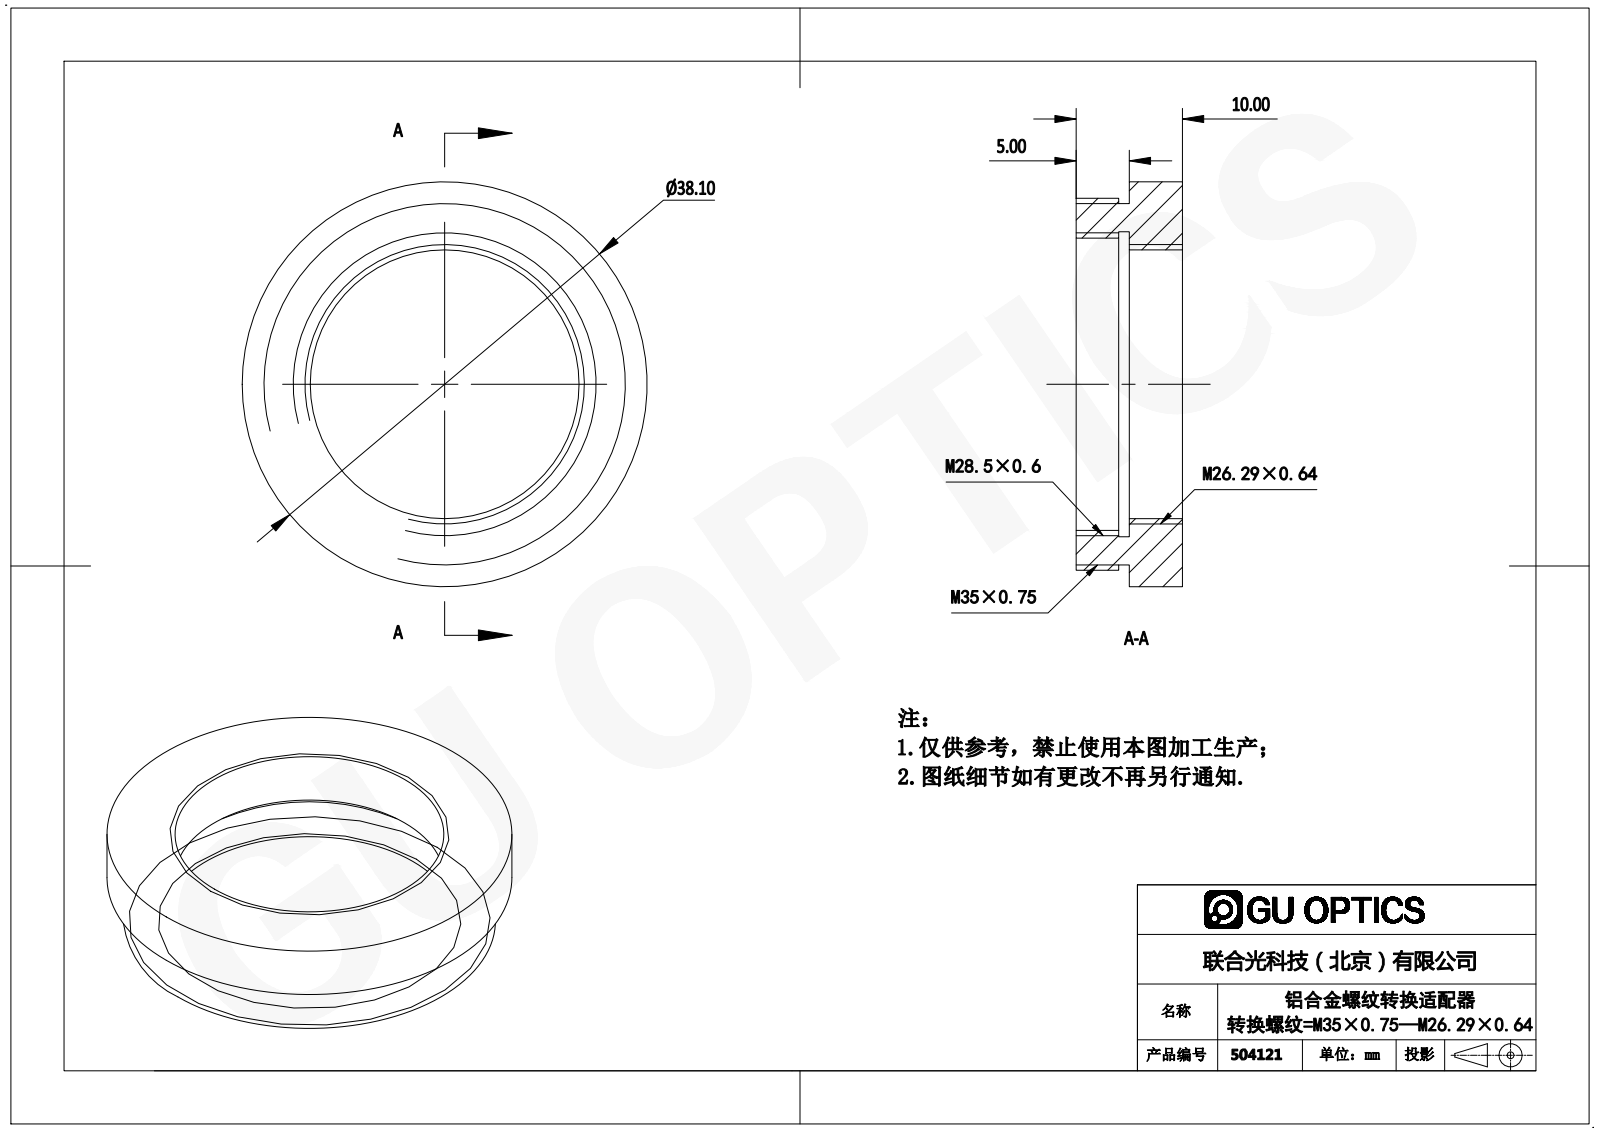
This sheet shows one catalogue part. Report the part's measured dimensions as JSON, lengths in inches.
{"part_name": "504121", "step_written_by": "SolidWorks 2016 (AUTOMOTIVE_DESIGN)", "units": "inches", "bodies": {"solids": 1, "faces": 18, "planar": 6, "cylindrical": 12, "other": 0}, "overall_size": [1.5, 1.5, 0.394], "volume_in3": 0.3, "surface_area_in2": 5.375, "round_holes": [[0.996, 1], [1.083, 1], [1.13, 1]], "round_bosses_or_shafts": [[1.5, 1], [1.378, 1], [1.339, 1]], "face_to_face_distances": [0.197, 0.394, 0.157, 0.039, 0.236]}
